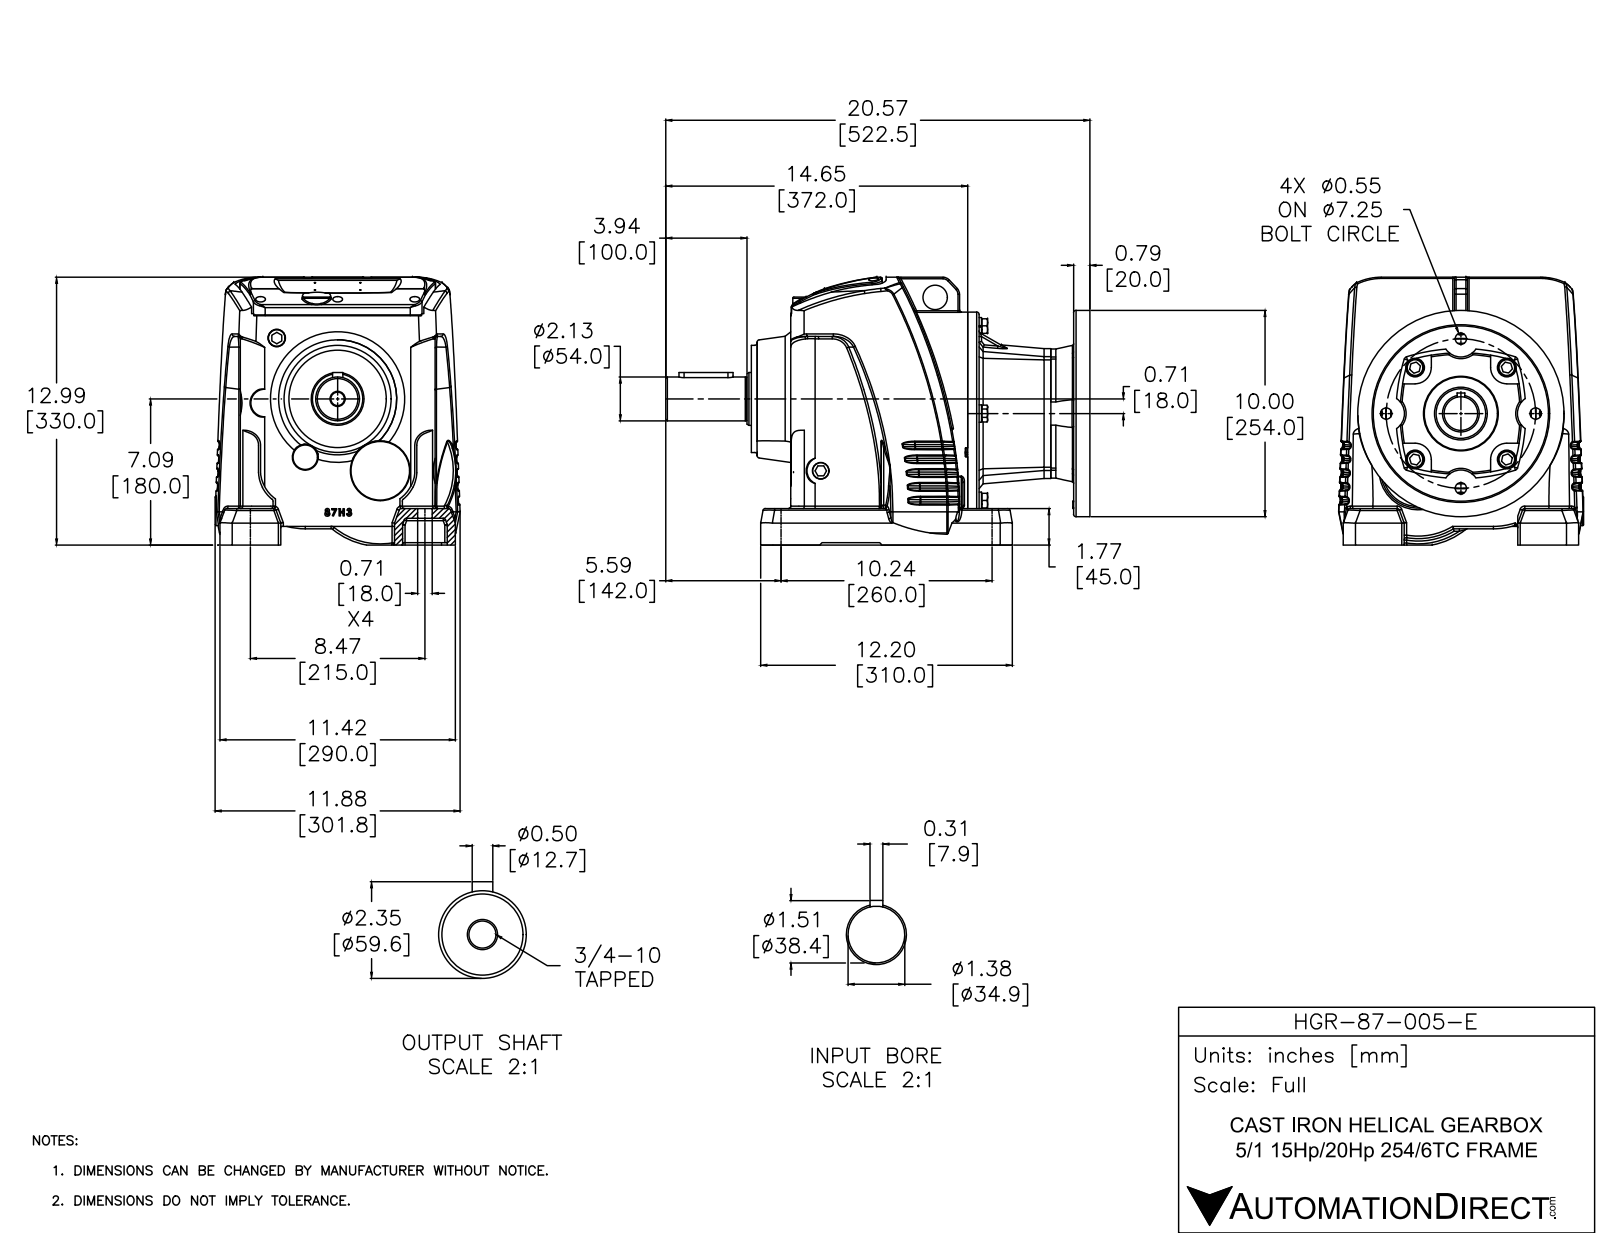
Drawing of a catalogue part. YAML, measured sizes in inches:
part_name: "HGR-87-005-E"
step_written_by: "SolidWorks 2017 (AUTOMOTIVE_DESIGN)"
units: inches
bodies: {solids: 29, faces: 1389, planar: 326, cylindrical: 321, other: 742}
overall_size: [20.571, 12.992, 11.882]
volume: 1238
surface_area: 1700
round_holes:
  - {diameter: 0.472, count: 7}
  - {diameter: 0.079, count: 4}
  - {diameter: 0.551, count: 4}
  - {diameter: 0.709, count: 4}
  - {diameter: 0.906, count: 4}
  - {diameter: 0.839, count: 3}
  - {diameter: 2.559, count: 2}
  - {diameter: 0.656, count: 1}
  - {diameter: 0.703, count: 1}
  - {diameter: 0.878, count: 1}
  - {diameter: 1.181, count: 1}
  - {diameter: 1.378, count: 1}
round_bosses_or_shafts:
  - {diameter: 0.866, count: 5}
  - {diameter: 0.846, count: 4}
  - {diameter: 0.827, count: 4}
  - {diameter: 0.394, count: 4}
  - {diameter: 10, count: 1}
  - {diameter: 9.843, count: 1}
  - {diameter: 5.494, count: 1}
  - {diameter: 5.197, count: 1}
partial_cylinders:
  - {radius: 0.118, count: 64}
  - {radius: 0.079, count: 12}
  - {radius: 0.591, count: 10}
  - {radius: 0.157, count: 4}
  - {radius: 0.394, count: 4}
  - {radius: 0.5, count: 4}
  - {radius: 0.709, count: 4}
  - {radius: 0.748, count: 4}
face_to_face_distances: [4.035, 0.039, 0.394, 8.465, 8.583, 0.591, 2.559, 9.6, 0.551, 12.618]
hole_center_spacings: [2.63, 6.262, 3.15, 3.625, 4.454, 5.127, 2.874, 1.207]
